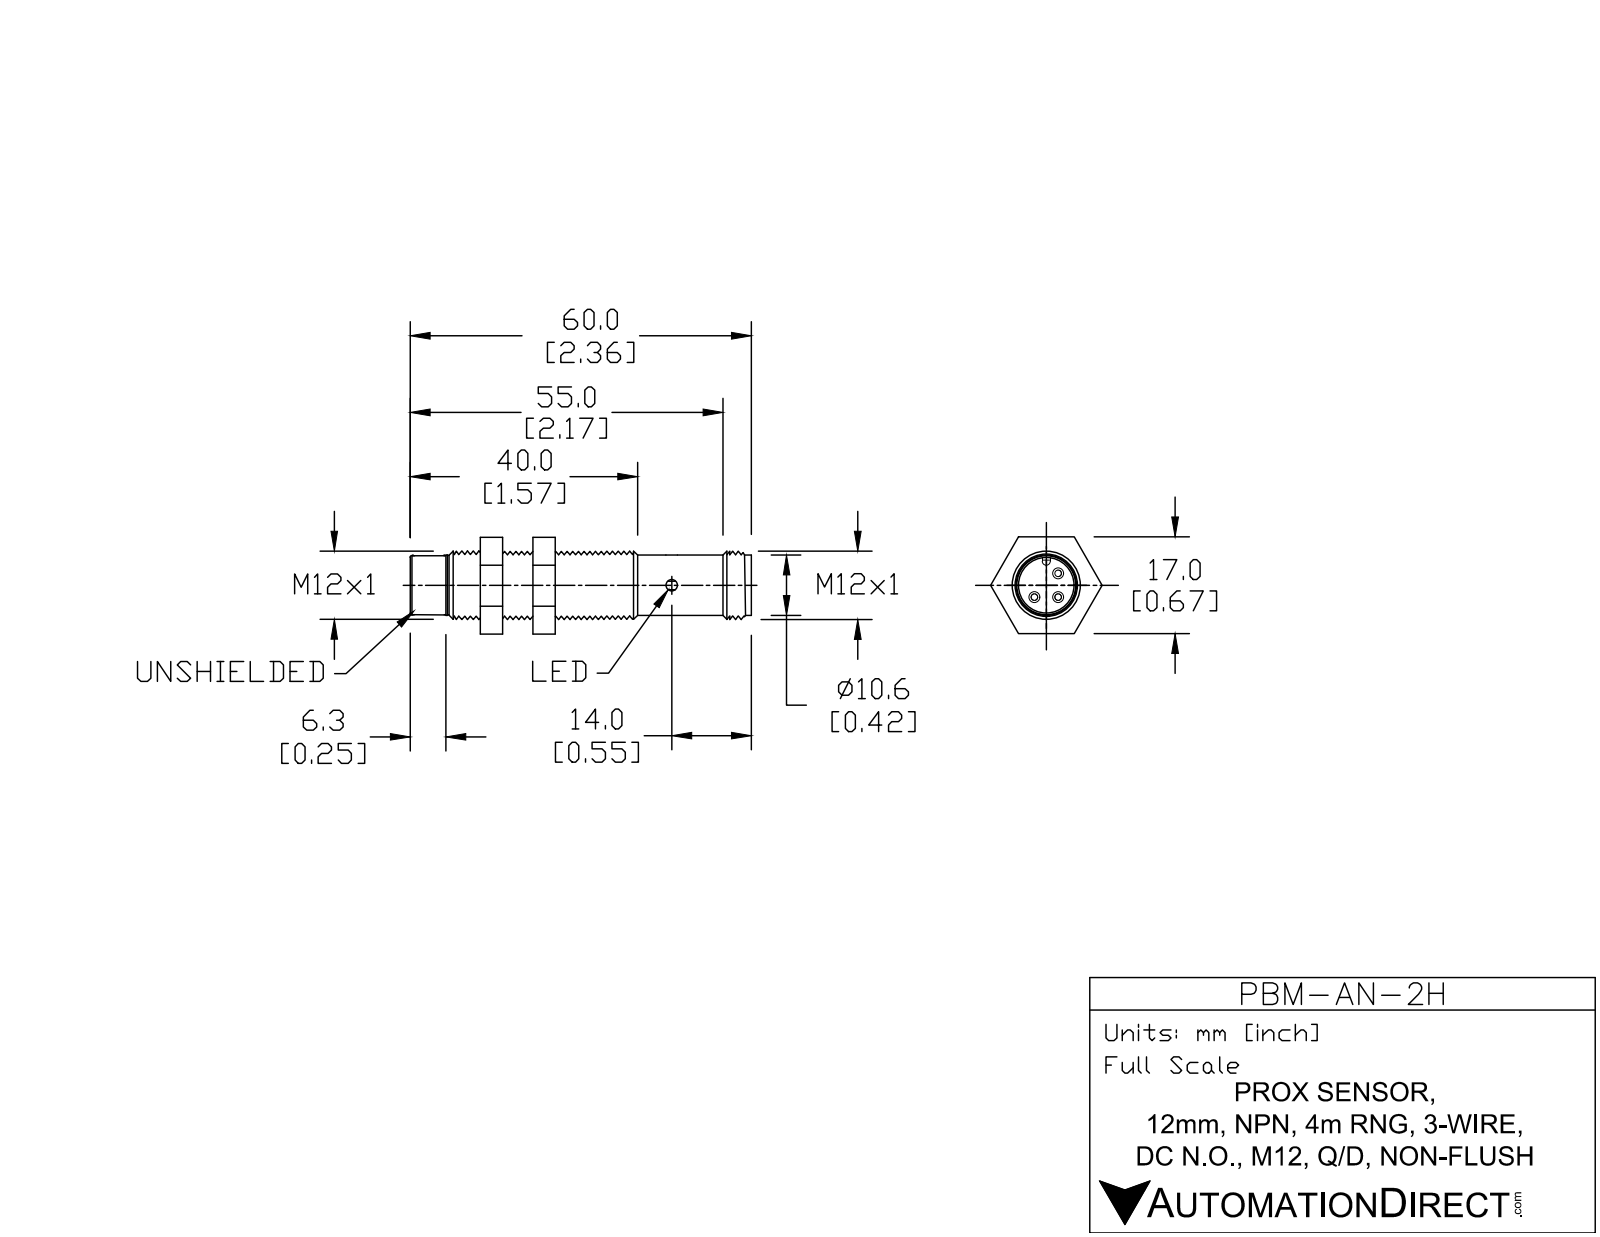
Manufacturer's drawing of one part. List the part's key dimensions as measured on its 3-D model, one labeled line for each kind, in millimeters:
Part name (STEP PRODUCT): PBM-AN-2H
STEP written by: SolidWorks 2011 (AUTOMOTIVE_DESIGN)
Units: millimetres
Bodies: 9 solids, 66 faces (38 planar, 17 cylindrical, 11 other)
Overall size (bounding box): 60 × 19.63 × 17.11
Volume: 6 905 mm³ · Surface area: 4 985 mm²
Round holes (diameter × count): ⌀1.5 ×1, ⌀3.5 ×1, ⌀8.4 ×1, ⌀10.25 ×1, ⌀12 ×1
Round bosses / shafts (diameter × count): ⌀1 ×3, ⌀10.75 ×1, ⌀10.62 ×1, ⌀10.5 ×1
Partial cylindrical surfaces — rounded edges, fillets, slot ends (radius × count): R0.5 ×1
Main face-to-face distances: 17, 10, 4, 22, 6, 32, 28, 26, 16, 12
